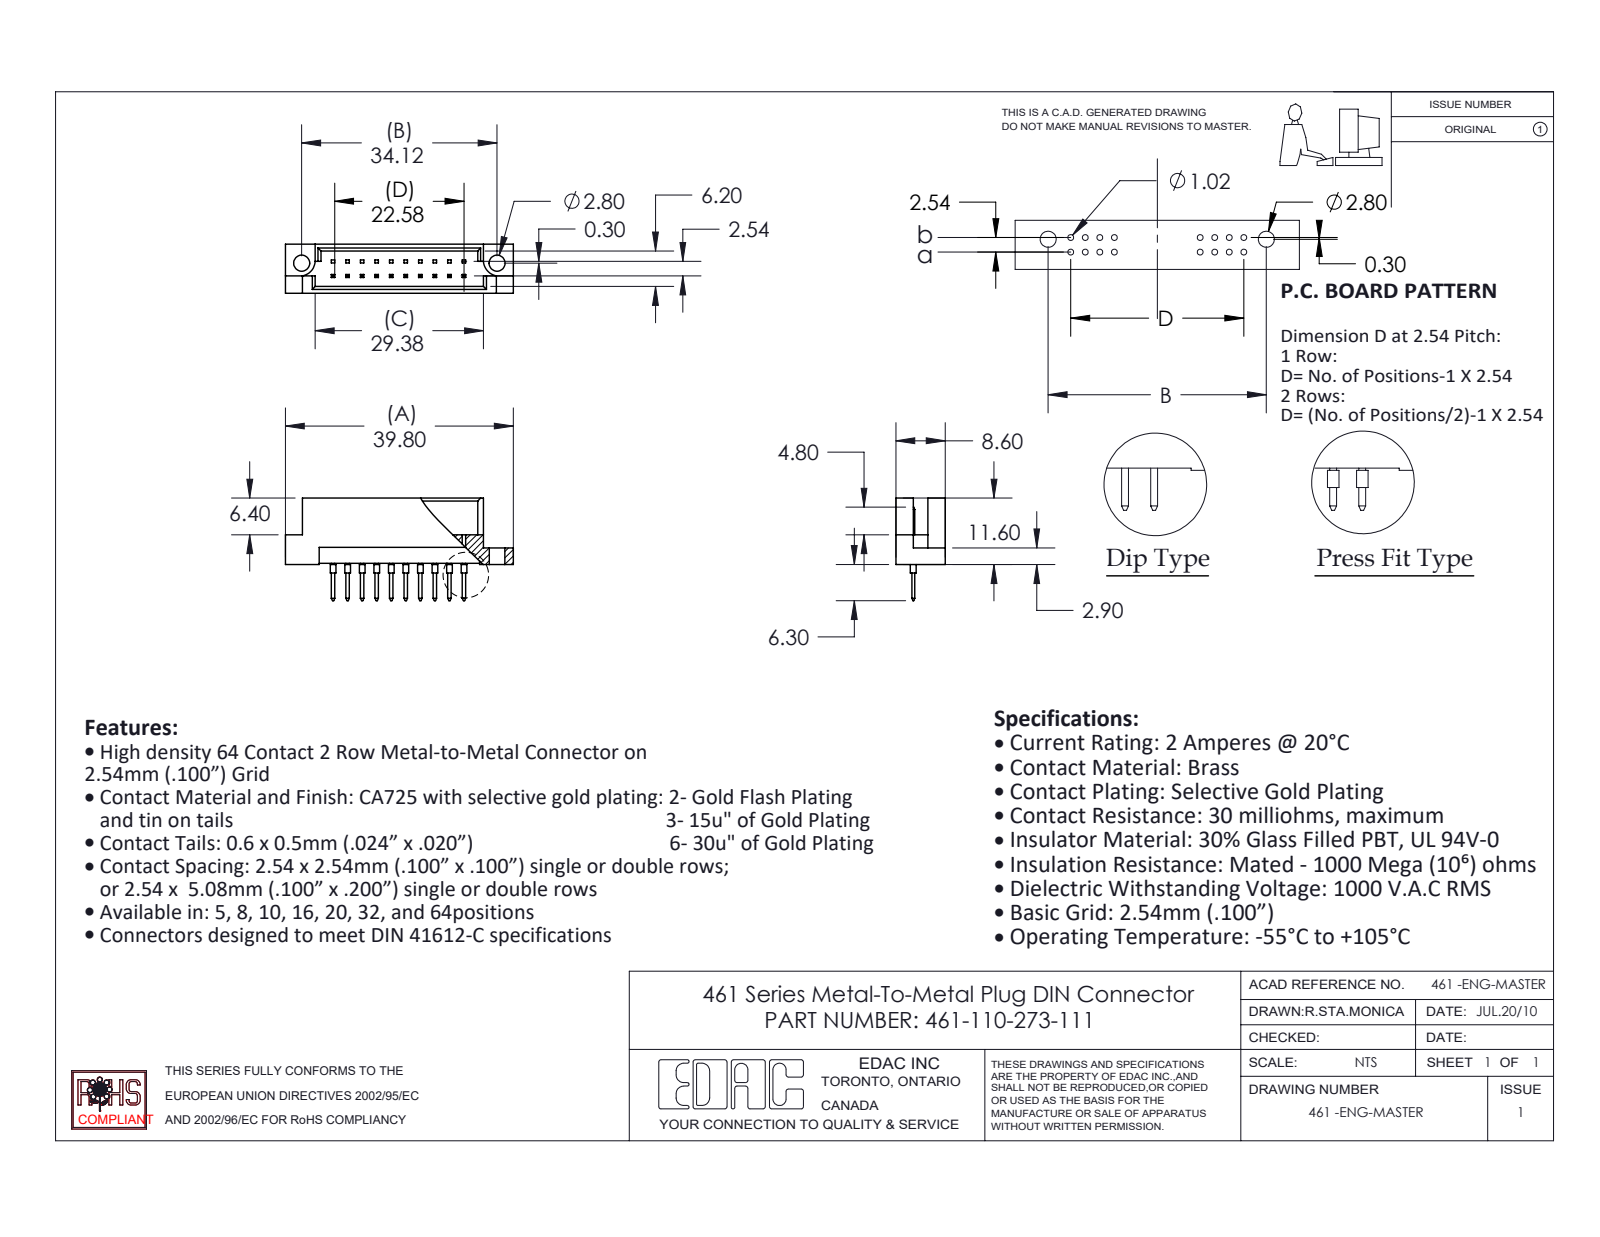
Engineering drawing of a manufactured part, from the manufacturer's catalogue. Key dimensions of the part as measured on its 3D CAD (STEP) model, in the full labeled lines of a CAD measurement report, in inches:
Part name (STEP PRODUCT): 461 Part_20; 461-290_73; 461-110-273-111
STEP written by: SolidWorks 2020 (CONFIG_CONTROL_DESIGN)
Units: inches
Bodies: 11 solids, 348 faces (322 planar, 26 cylindrical, 0 other)
Overall size (bounding box): 1.567 × 0.705 × 0.339
Volume: 0.12 in³ · Surface area: 4.21 in²
Round holes (diameter × count): ⌀0.11 ×2
Round bosses / shafts (diameter × count): ⌀0.039 ×10
Partial cylindrical surfaces — rounded edges, fillets, slot ends (radius × count): R0.11 ×2
Main face-to-face distances: 0.047, 0.291, 0.339, 0.244, 0.1, 0.197, 0.109, 0.129, 0.209, 0.229
Hole centre spacings: 1.343
